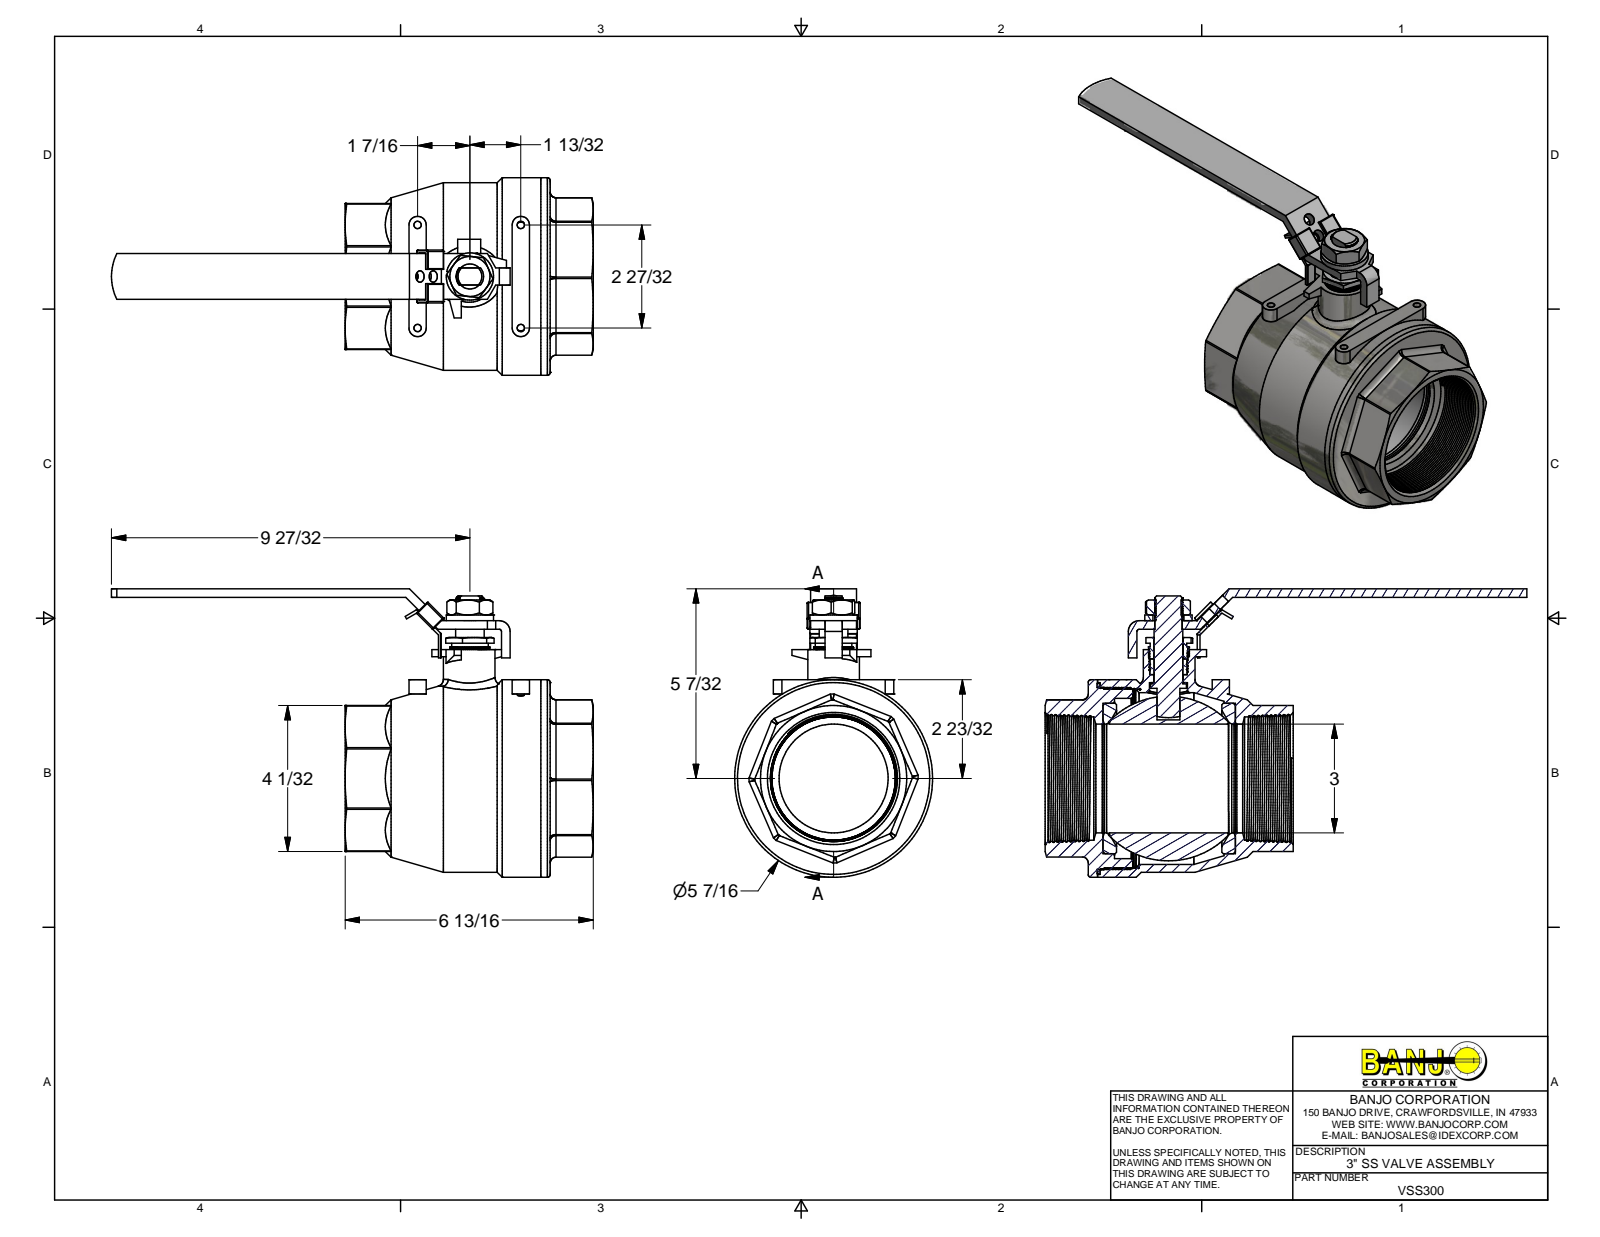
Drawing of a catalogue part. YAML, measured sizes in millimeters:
part_name: "VSS300"
step_written_by: "Autodesk Inventor 2013 (AUTOMOTIVE_DESIGN)"
units: millimeters
bodies: {solids: 14, faces: 531, planar: 158, cylindrical: 168, other: 205}
overall_size: [336, 201.5, 138]
volume: 1090000
surface_area: 316836
round_holes:
  - {diameter: 5.11, count: 4}
  - {diameter: 8, count: 2}
  - {diameter: 9, count: 1}
  - {diameter: 17.46, count: 1}
  - {diameter: 20, count: 1}
  - {diameter: 20.5, count: 1}
  - {diameter: 21.6, count: 1}
  - {diameter: 26.1, count: 1}
  - {diameter: 26.5, count: 1}
  - {diameter: 76, count: 1}
  - {diameter: 112, count: 1}
  - {diameter: 120, count: 1}
round_bosses_or_shafts:
  - {diameter: 138, count: 1}
  - {diameter: 133, count: 1}
  - {diameter: 131, count: 1}
  - {diameter: 127, count: 1}
  - {diameter: 105, count: 1}
  - {diameter: 36, count: 1}
  - {diameter: 33, count: 1}
  - {diameter: 27.8, count: 1}
partial_cylinders:
  - {radius: 0.5, count: 17}
  - {radius: 1, count: 9}
  - {radius: 1.5, count: 9}
  - {radius: 4, count: 8}
  - {radius: 6, count: 4}
  - {radius: 7.5, count: 1}
  - {radius: 9.53, count: 1}
  - {radius: 9.55, count: 1}
face_to_face_distances: [6, 92.4, 6.5, 2, 102.7, 10.3, 3.8, 96.2, 10, 40.3]
hole_center_spacings: [72, 13.05, 50.56, 51.27, 101.82]
